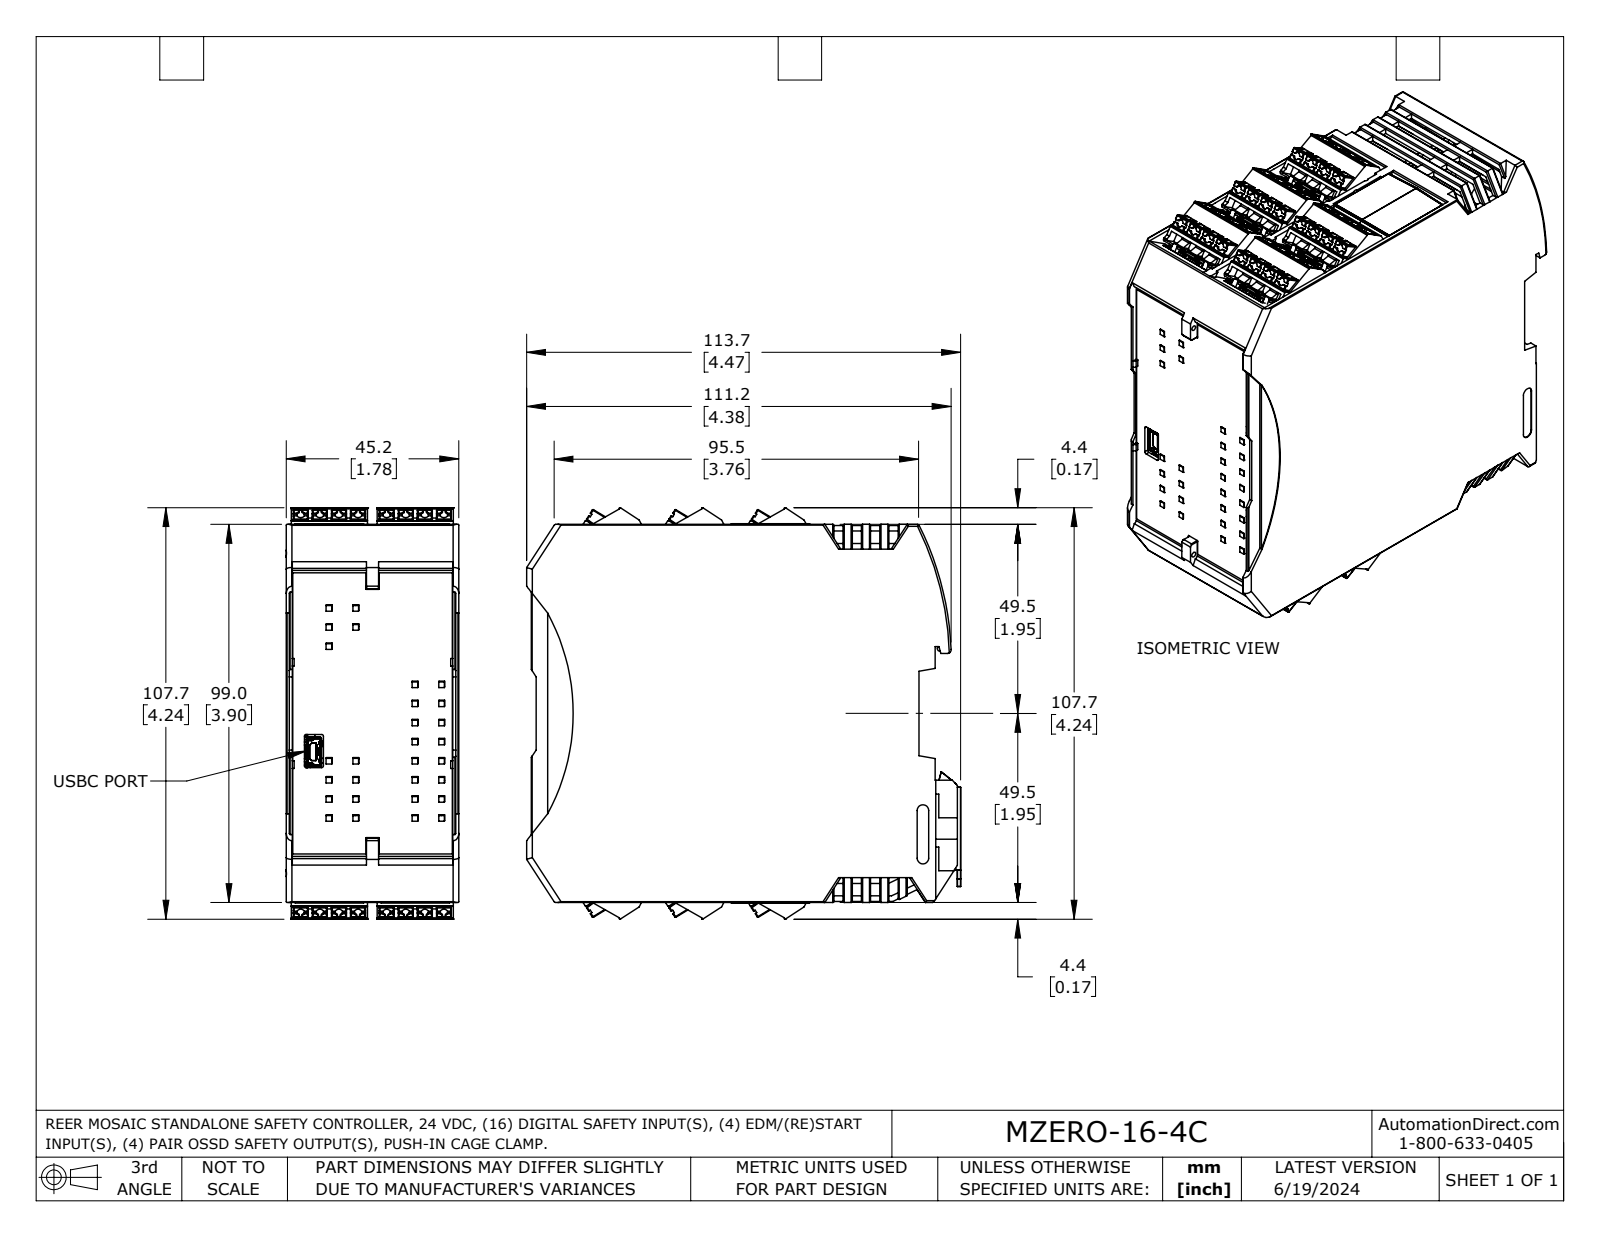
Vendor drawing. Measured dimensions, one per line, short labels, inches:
name: MZERO-16-4C
written by: SolidWorks 2023 (AUTOMOTIVE_DESIGN)
unit: in
bodies: 2 solids, 6746 faces (4645 planar, 1744 cylindrical, 357 other)
size: 4.474 × 4.242 × 1.78
volume: 24.72 in³; area: 146.5 in²
holes: 1× ⌀0.053, 1× ⌀0.055, 1× ⌀0.118
bosses: 2× ⌀0.031
rounds: 443× R0.008, 230× R0.02, 222× R0.012, 105× R0.004, 41× R0.039, 40× R0.047, 16× R0.055, 16× R0.059
face distances: 1.78, 0.039, 0.049, 1.73, 0.386, 3.499, 3.885, 3.846, 0.347, 3.386
hole spacings: 2.858, 3.002, 4.426
